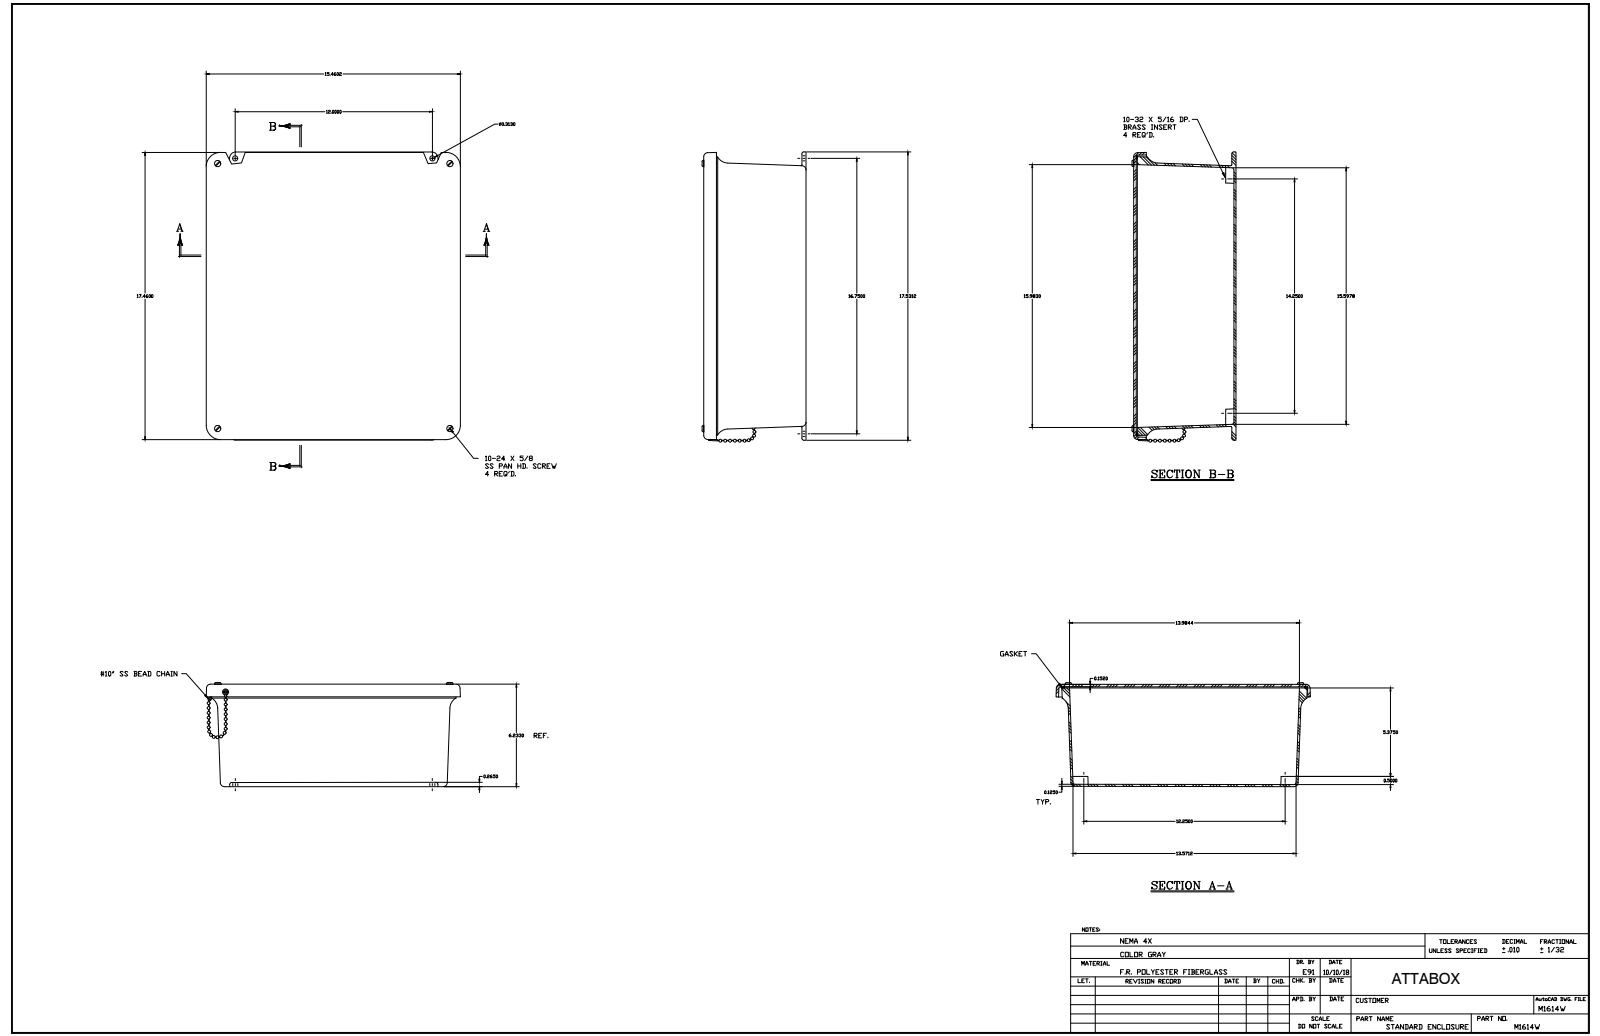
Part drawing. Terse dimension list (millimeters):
name: M1614W
written by: SolidWorks 2018 (AUTOMOTIVE_DESIGN)
unit: mm
bodies: 45 solids, 898 faces (191 planar, 295 cylindrical, 412 other)
size: 458.2 × 398.5 × 161
volume: 2 342 000 mm³; area: 1 221 000 mm²
holes: 8× ⌀3.9, 6× ⌀3.6, 4× ⌀3.7, 4× ⌀4, 4× ⌀5.5, 2× ⌀4.7, 1× ⌀3.2
bosses: 8× ⌀6.9, 4× ⌀4.8, 4× ⌀4, 2× ⌀9.5, 2× ⌀6.4, 2× ⌀3.2, 1× ⌀7.2
rounds: 20× R0.8, 12× R3.2, 12× R6.4, 8× R5.1, 4× R9.5, 4× R19.1, 2× R0.3, 2× R1.6
face distances: 3.2, 3.9, 153.8, 157.7, 150.7, 154.5, 3.2, 5.3, 152.4, 149.2
hole spacings: 33.6, 335.8, 386.3, 510.7, 95.3, 190.5, 311.2, 358.8
